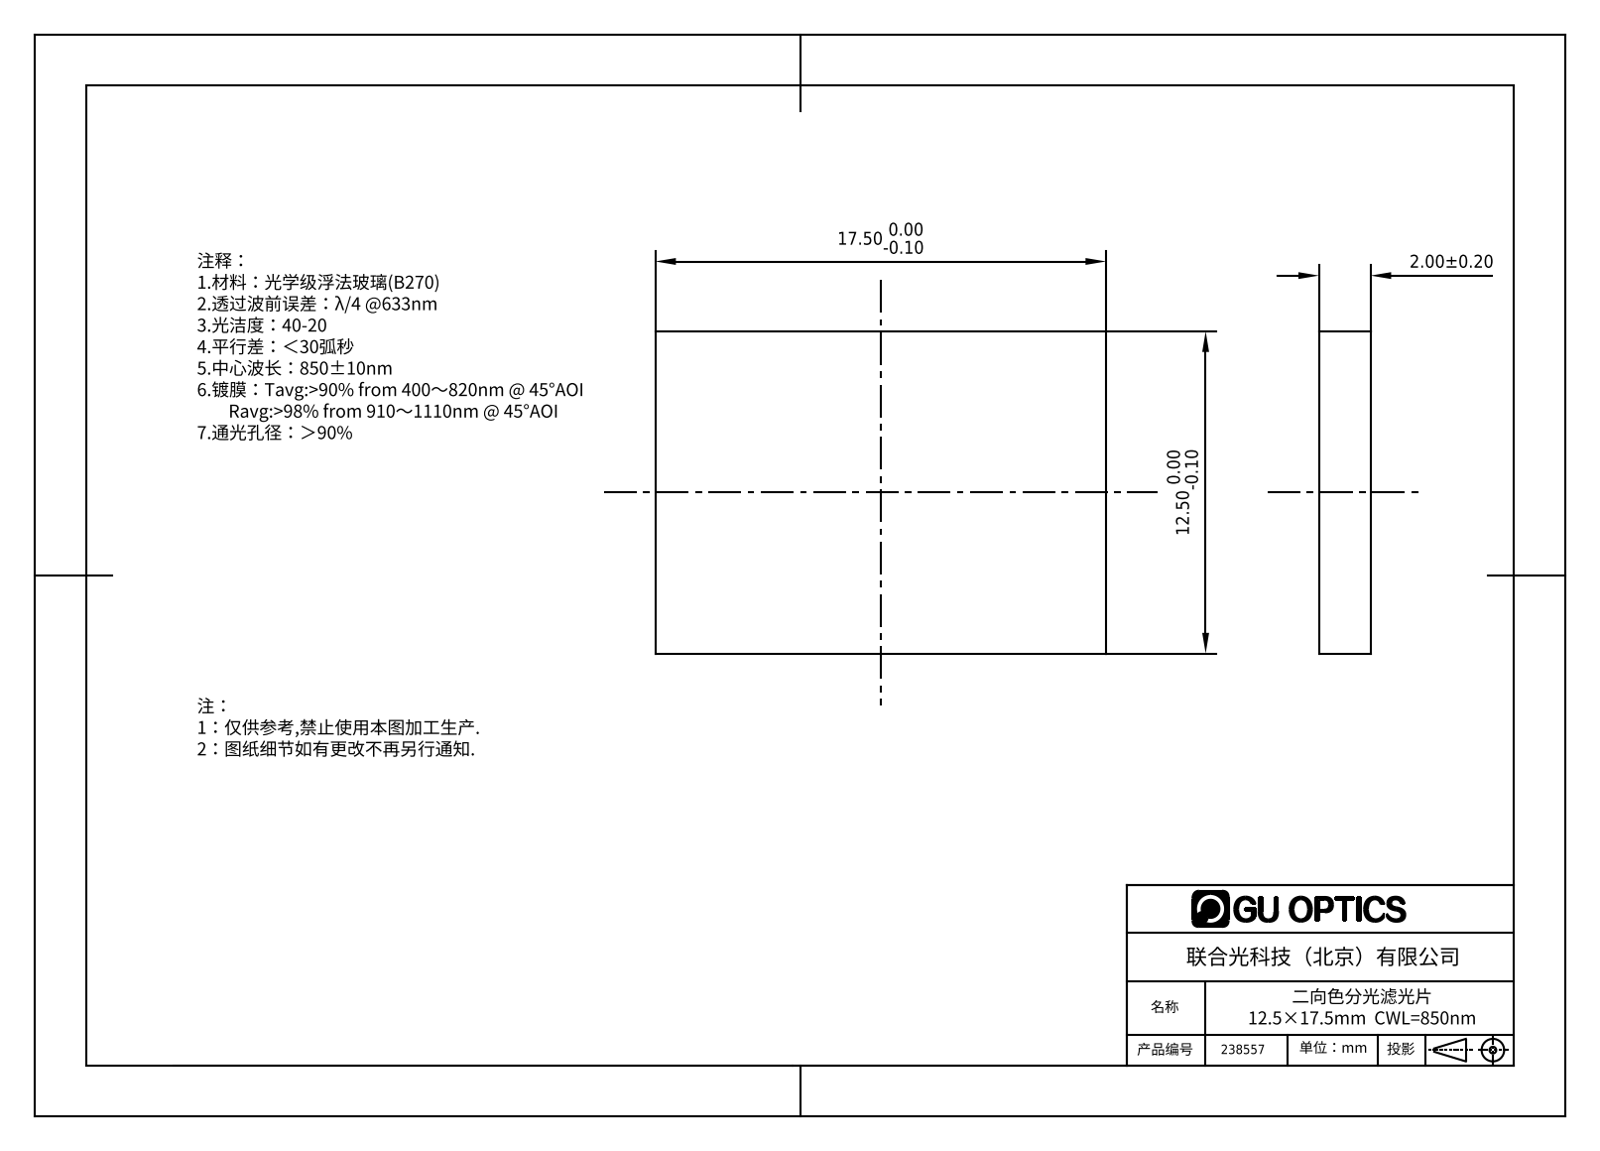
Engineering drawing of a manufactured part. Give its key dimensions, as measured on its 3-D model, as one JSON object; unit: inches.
{"part_name": "238510", "step_written_by": "SolidWorks 2016 (AUTOMOTIVE_DESIGN)", "units": "inches", "bodies": {"solids": 1, "faces": 6, "planar": 6, "cylindrical": 0, "other": 0}, "overall_size": [0.689, 0.492, 0.079], "volume_in3": 0.027, "surface_area_in2": 0.865, "face_to_face_distances": [0.079, 0.492, 0.689]}
